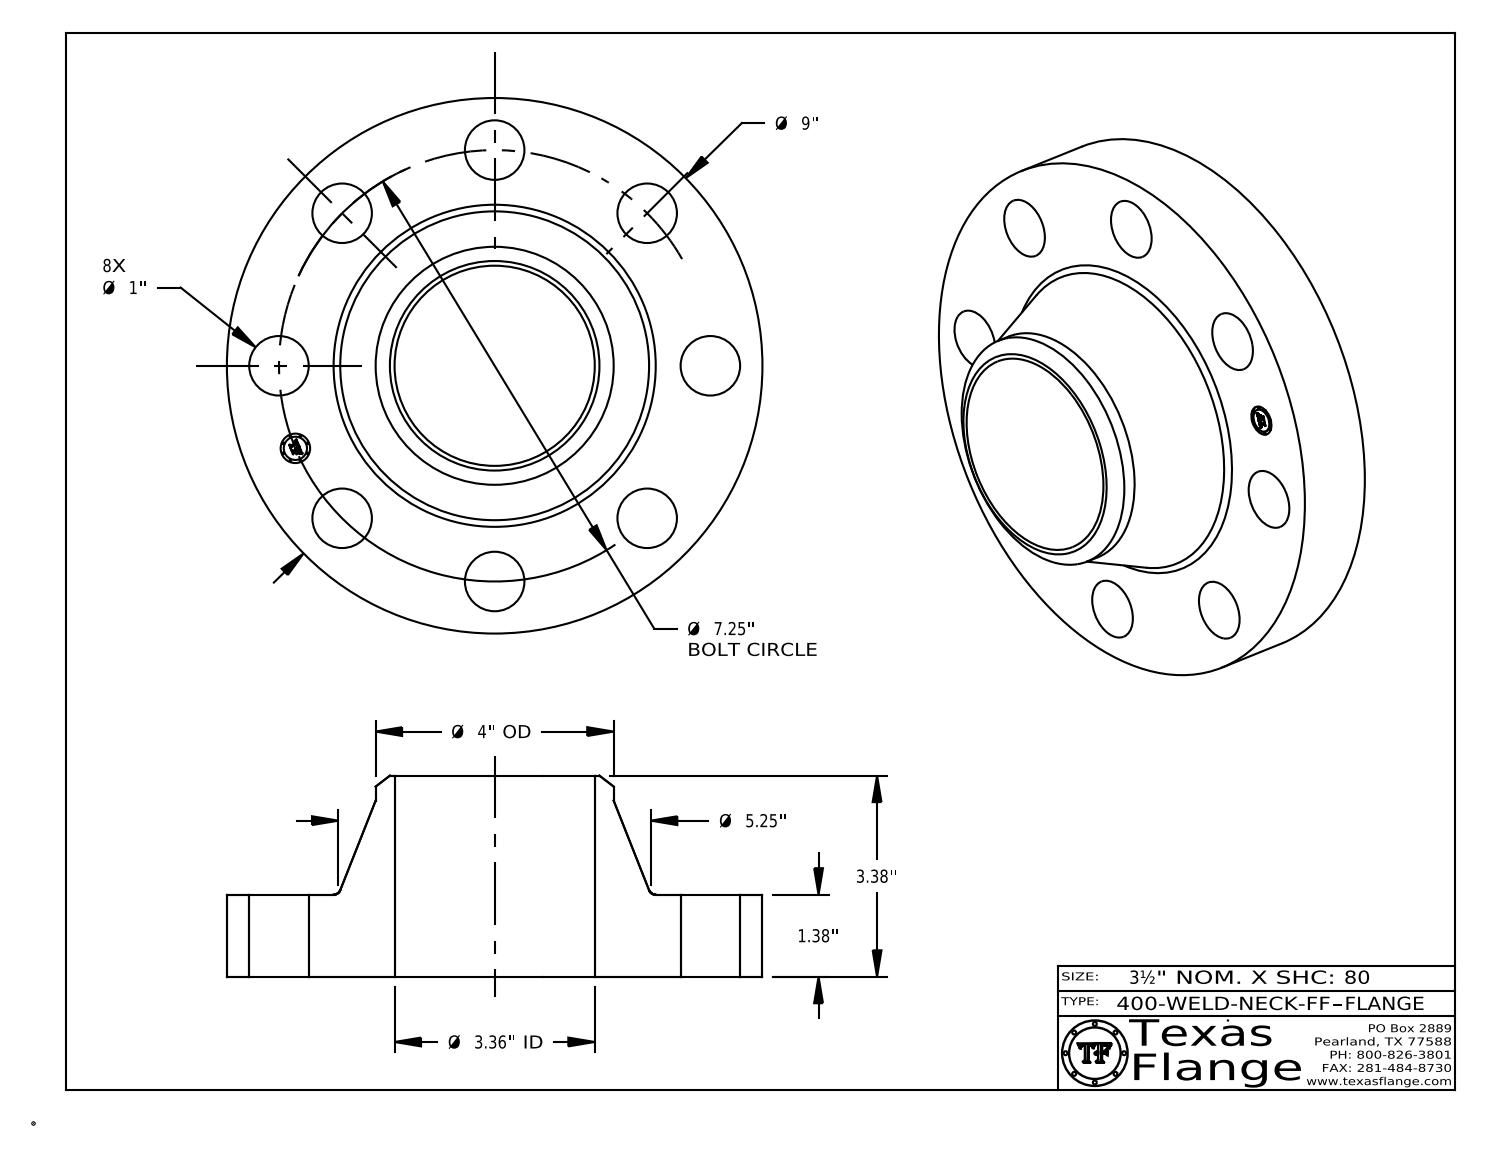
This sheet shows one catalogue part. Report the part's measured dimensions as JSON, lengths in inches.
{"part_name": "400-WELD-NECK-FF", "step_written_by": "CATIA V5 STEP AP214 (AUTOMOTIVE_DESIGN)", "units": "inches", "bodies": {"solids": 1, "faces": 416, "planar": 368, "cylindrical": 42, "other": 6}, "overall_size": [9, 9, 3.38], "volume_in3": 80.82, "surface_area_in2": 225.4, "round_holes": [[1, 8], [0.495, 1], [3.364, 1]], "round_bosses_or_shafts": [[0.03, 8], [9, 1], [4, 1], [0.39, 1]], "face_to_face_distances": [1.38, 3.38, 2, 1.365, 0.015, 2.015, 0.148, 0.144, 0.027, 0.096], "hole_center_spacings": [3.625, 2.774, 5.127, 6.698, 7.25, 1.415, 7.111, 4.028]}
